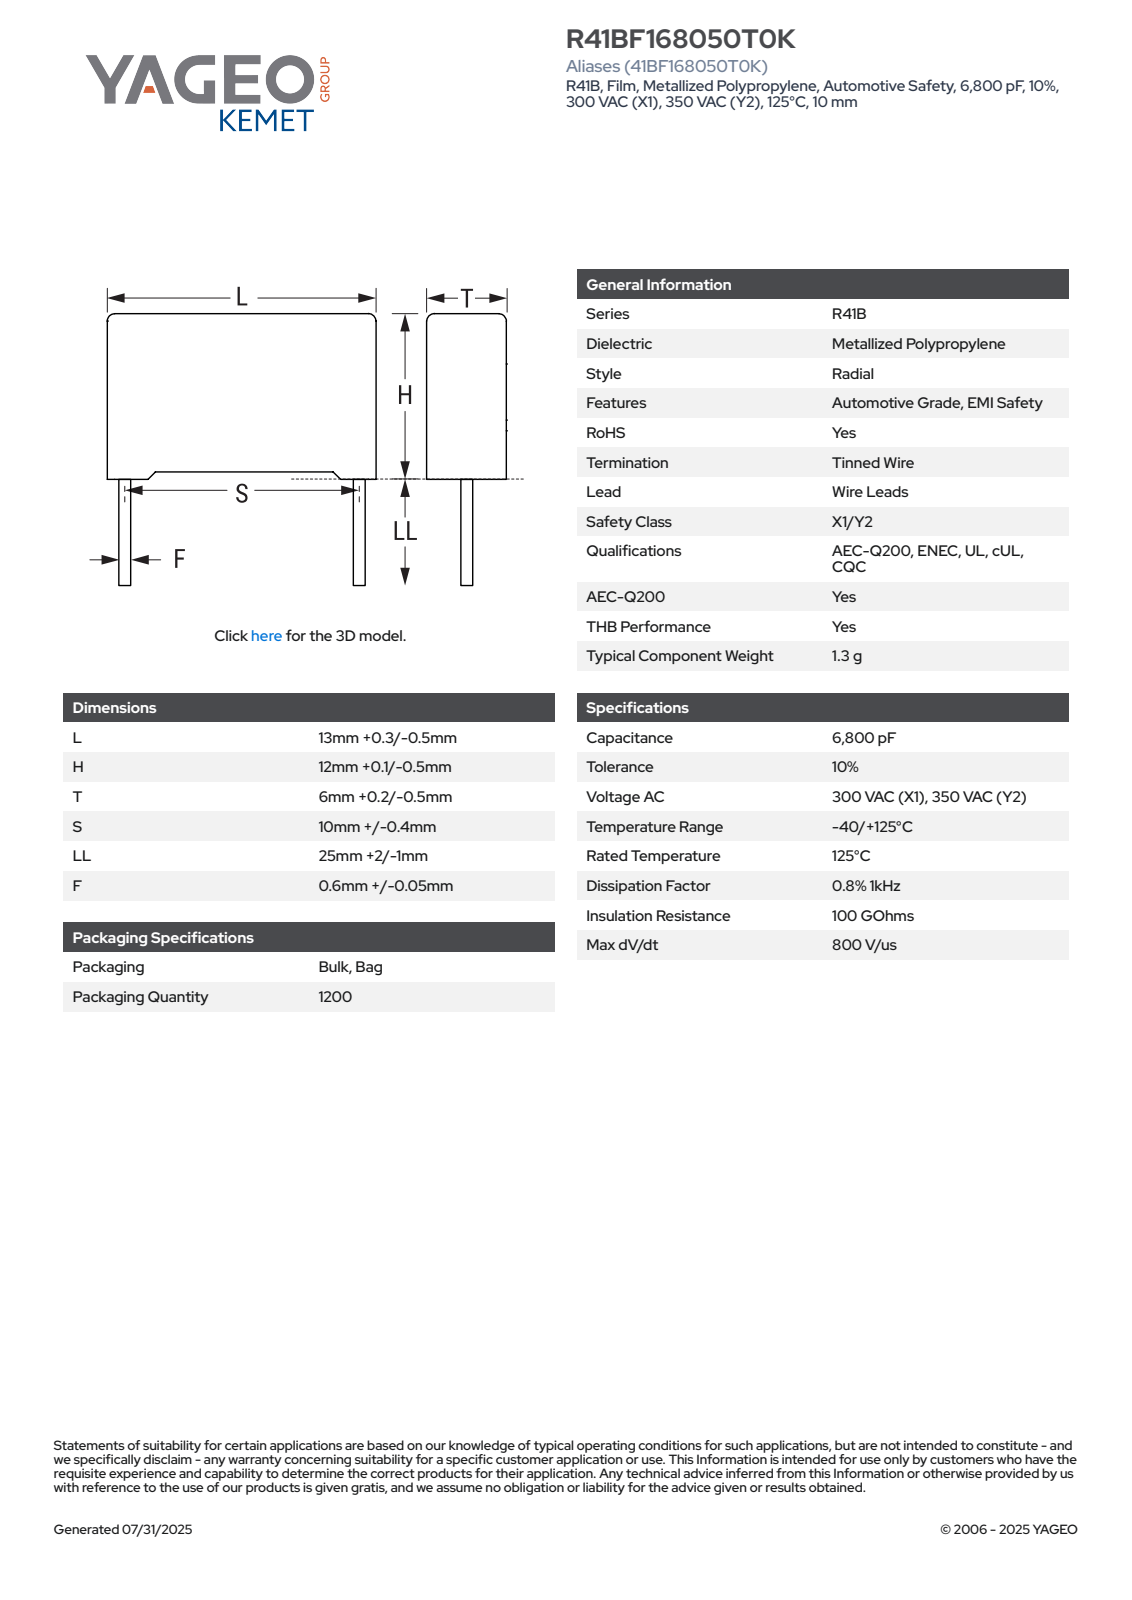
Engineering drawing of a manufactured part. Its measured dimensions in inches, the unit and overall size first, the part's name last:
Units: inches
Overall size (bounding box): 1.539 × 0.524 × 0.244
Round bosses / shafts (diameter × count): ⌀0.026 ×2
Partial cylindrical surfaces — rounded edges, fillets, slot ends (radius × count): R0.02 ×4
Main face-to-face distances: 0.244, 0.524, 0.447, 0.017, 0.227, 0.03, 0.476, 0.506, 0.209, 0.017
Volume: 0.059 in³ · Surface area: 1.2 in²
Bodies: 4 solids, 85 faces (77 planar, 8 cylindrical, 0 other)
Part name (STEP PRODUCT): CFR_RB2_13X12X6_L13.3H12.1T6.2S10LL27F0.65
STEP written by: SolidWorks 2021 (AUTOMOTIVE_DESIGN)
